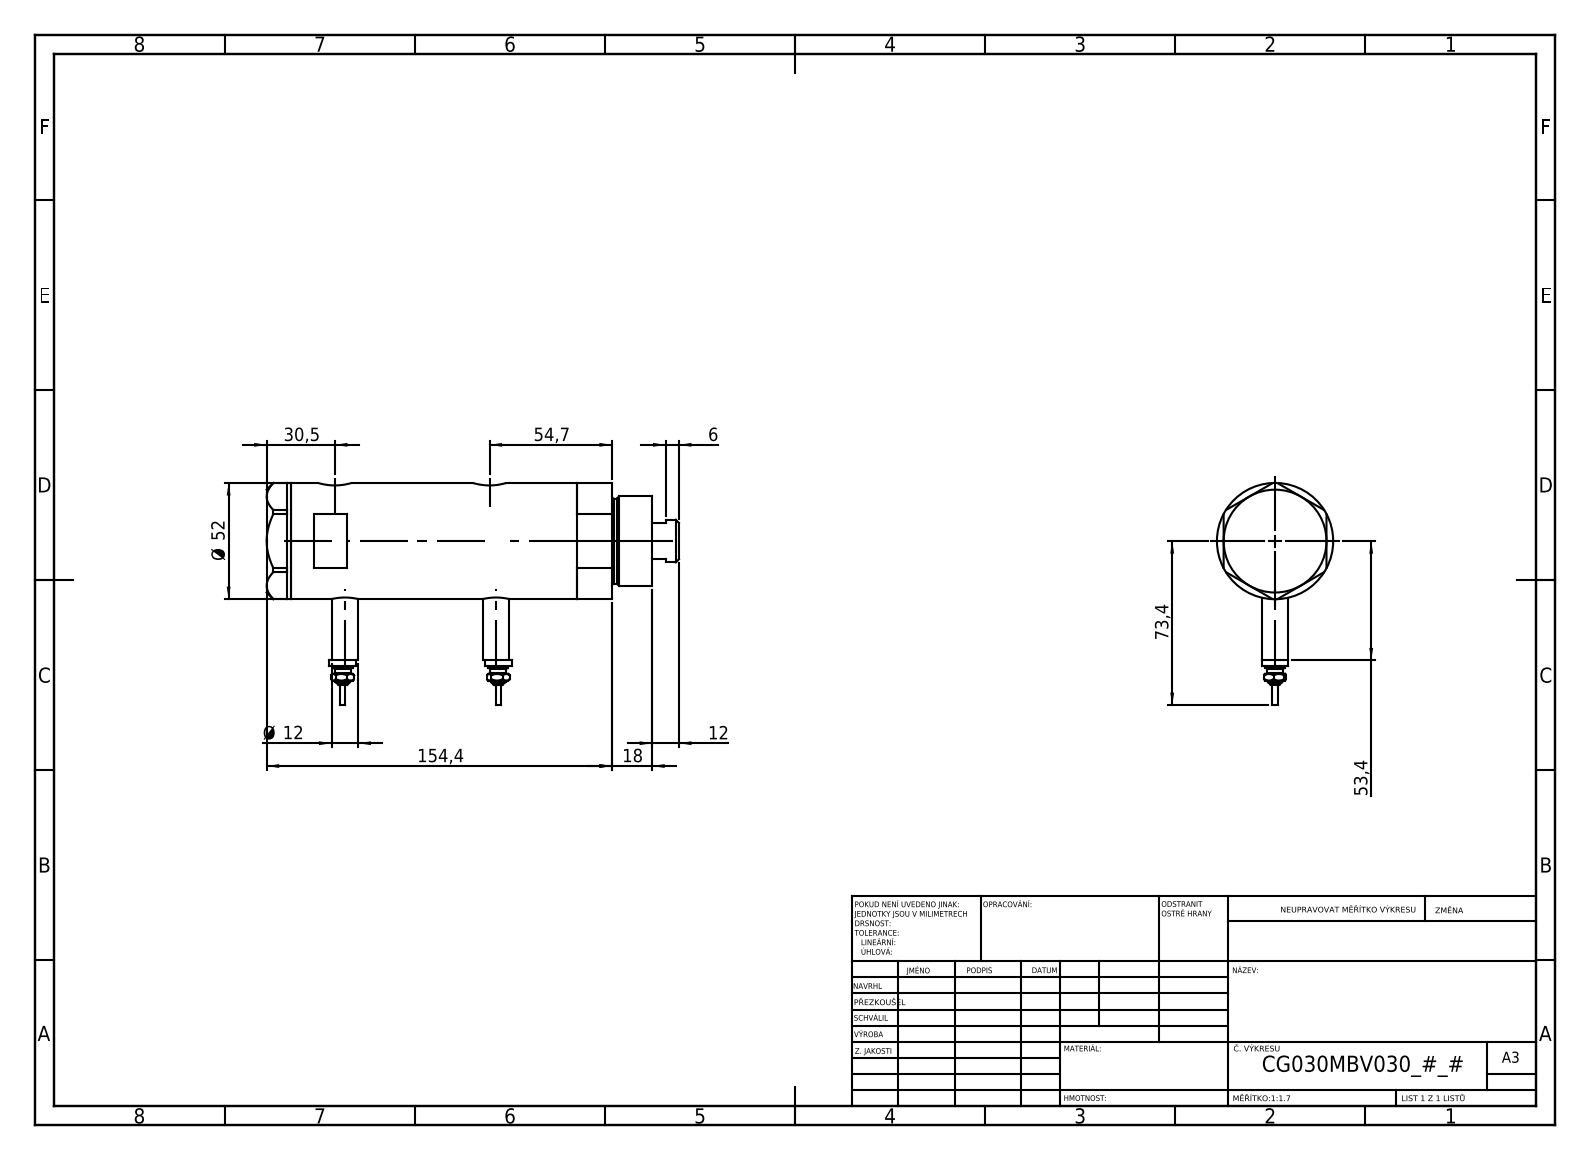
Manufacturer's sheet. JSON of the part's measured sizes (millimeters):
{"part_name": "V270CG_MIDDLE; Switch; V270CG_VC; V270CG_BACK (+1 more)", "step_written_by": "SolidWorks 2019 (CONFIG_CONTROL_DESIGN)", "units": "millimeters", "bodies": {"solids": 6, "faces": 226, "planar": 93, "cylindrical": 69, "other": 64}, "overall_size": [184.4, 99.4, 52], "volume_mm3": 340934, "surface_area_mm2": 79913, "round_holes": [[9.73, 2], [12.5, 2], [15, 2], [6.5, 1], [20, 1], [21.5, 1], [30, 1], [33, 1], [44, 1]], "round_bosses_or_shafts": [[12, 4], [9, 2], [7, 2], [4.5, 2], [2.5, 2], [52, 1], [40, 1], [38, 1]], "face_to_face_distances": [91.5, 23.8, 67.7, 11, 34.8, 102.5, 46, 36.4, 138.9, 127.9], "hole_center_spacings": [2.9, 4.5, 64.7, 67.6, 69.2, 72.1]}
